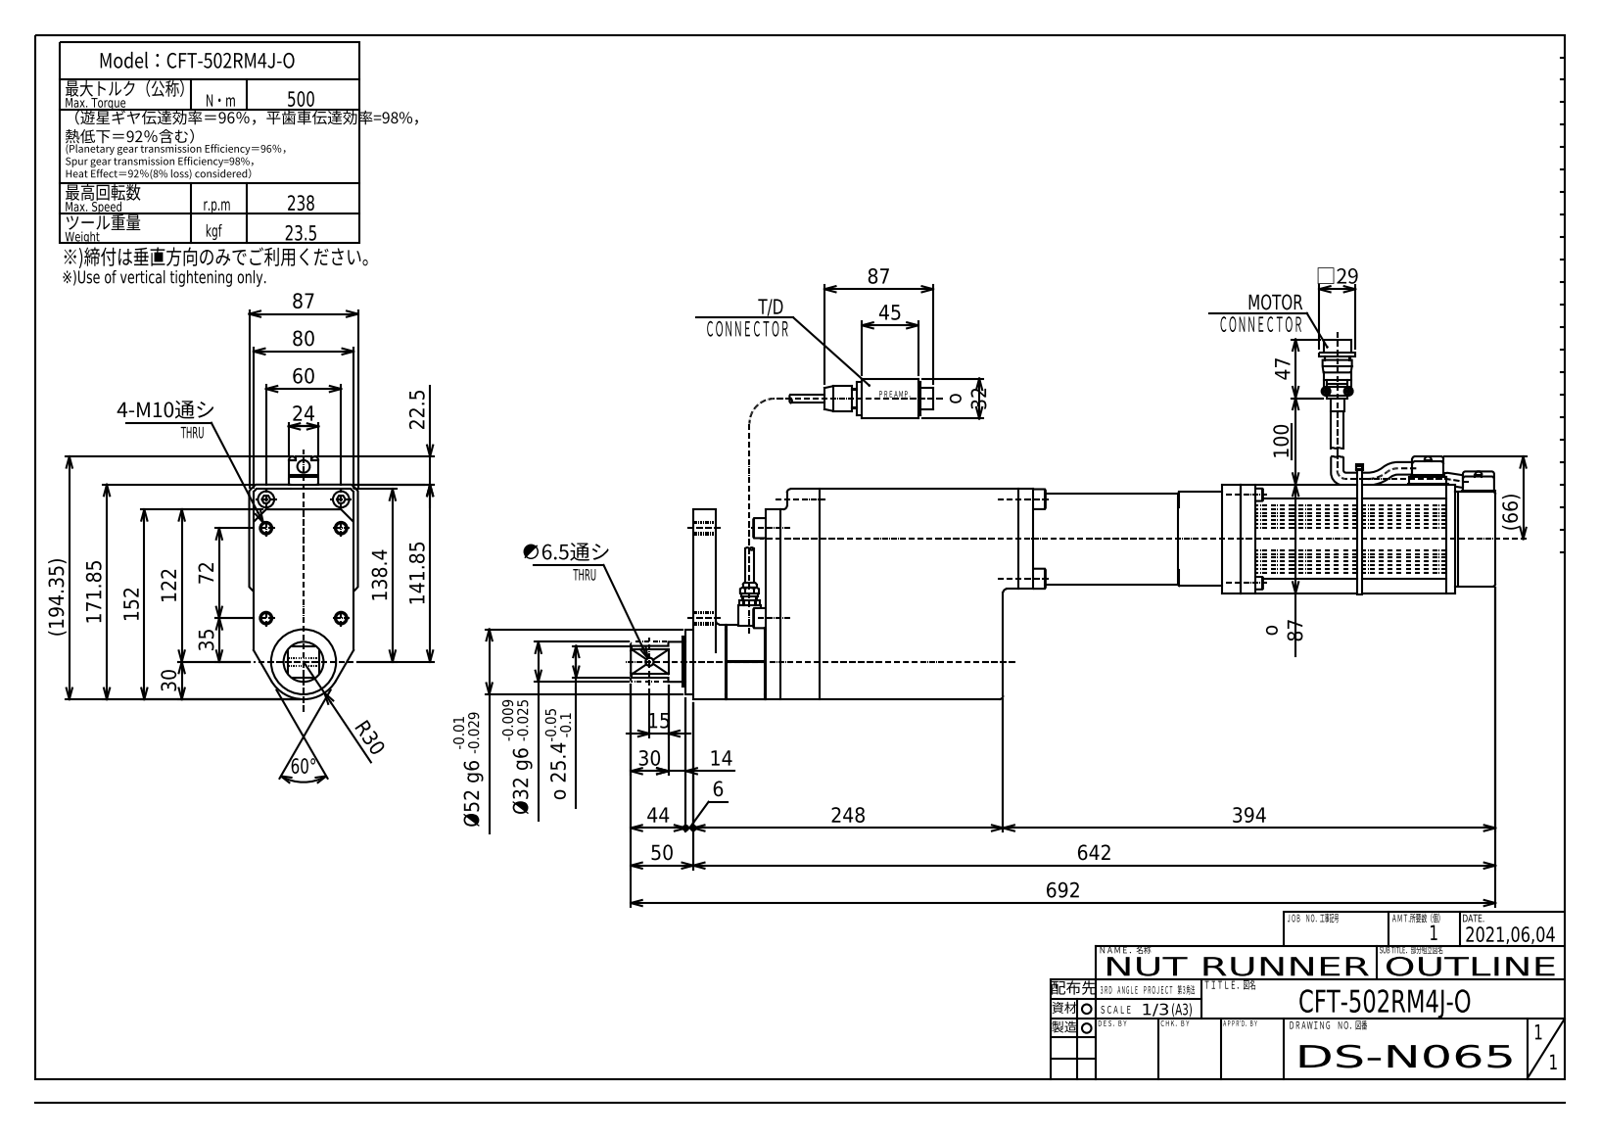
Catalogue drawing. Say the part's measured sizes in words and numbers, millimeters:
The part is named "CFT-502RM4J-O(DS-N065)_OUTLINE_20210803". Its 3-D file was written by "Autodesk Inventor 2021 (AUTOMOTIVE_DESIGN)". It is 1 solid with 1087 faces: 663 planar, 254 cylindrical and 170 other. Overall it measures 692 by 271.5 by 89 millimeters. Its volume is 5 004 000 cubic millimeters and its surface area 361 502 square millimeters. Round holes: 5 of diameter 6.5, 4 of diameter 5, 4 of diameter 8.5, 2 of diameter 2.5, 2 of diameter 8, 2 of diameter 14, 1 of diameter 42. Round bosses or shafts: 9 of diameter 16, 6 of diameter 8, 6 of diameter 7, 5 of diameter 10, 4 of diameter 8.5, 4 of diameter 7.5, 2 of diameter 13, 1 of diameter 80. Partial cylindrical surfaces (rounded edges, fillets, slot ends): 48 of radius 0.6, 26 of radius 1, 13 of radius 3, 11 of radius 0.5, 7 of radius 1.5, 6 of radius 5, 4 of radius 0.3, 4 of radius 2. The main face-to-face distances are 3, 1.5, 80, 4.5, 6, 3.5, 45, 46.5, 43.5, 7.5. The hole center spacings are 70.72, 60, 6.52, 17.65, 23, 27.24, 28.5, 31.8.
